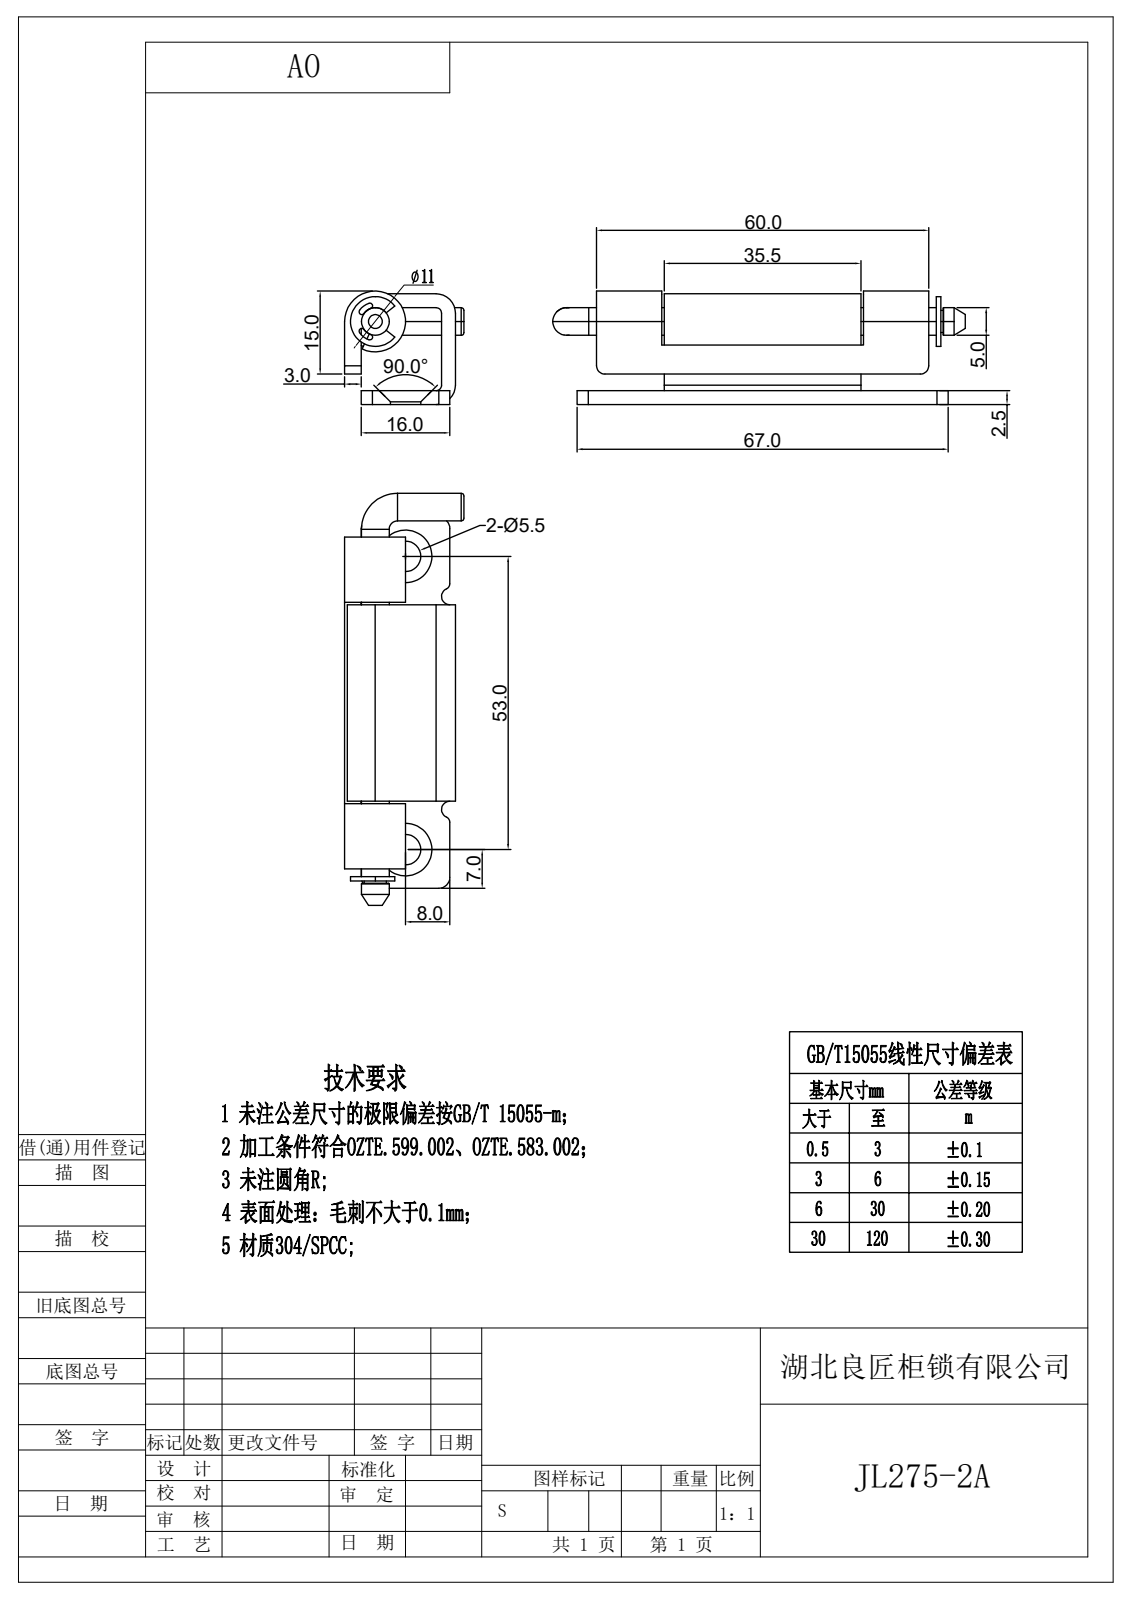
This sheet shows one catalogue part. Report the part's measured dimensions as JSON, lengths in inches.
{"step_written_by": "Rhino 8.5 (CONFIG_CONTROL_DESIGN)", "units": "inches", "bodies": {"solids": 4, "faces": 96, "planar": 36, "cylindrical": 46, "other": 14}, "overall_size": [2.933, 0.848, 0.807], "volume_in3": 0.679, "surface_area_in2": 15.71, "round_holes": [[0.217, 2], [0.157, 1], [0.197, 1]], "round_bosses_or_shafts": [[0.197, 2], [0.433, 1], [0.394, 1]], "partial_cylinders_radius": [[0.02, 4], [0.039, 4], [0.059, 4], [0.079, 4], [0.138, 3], [0.177, 1]], "face_to_face_distances": [0.098, 0.689, 0.787, 0.571, 0.118, 0.669, 0.591, 0.482, 1.88, 0.217], "hole_center_spacings": [2.087]}
